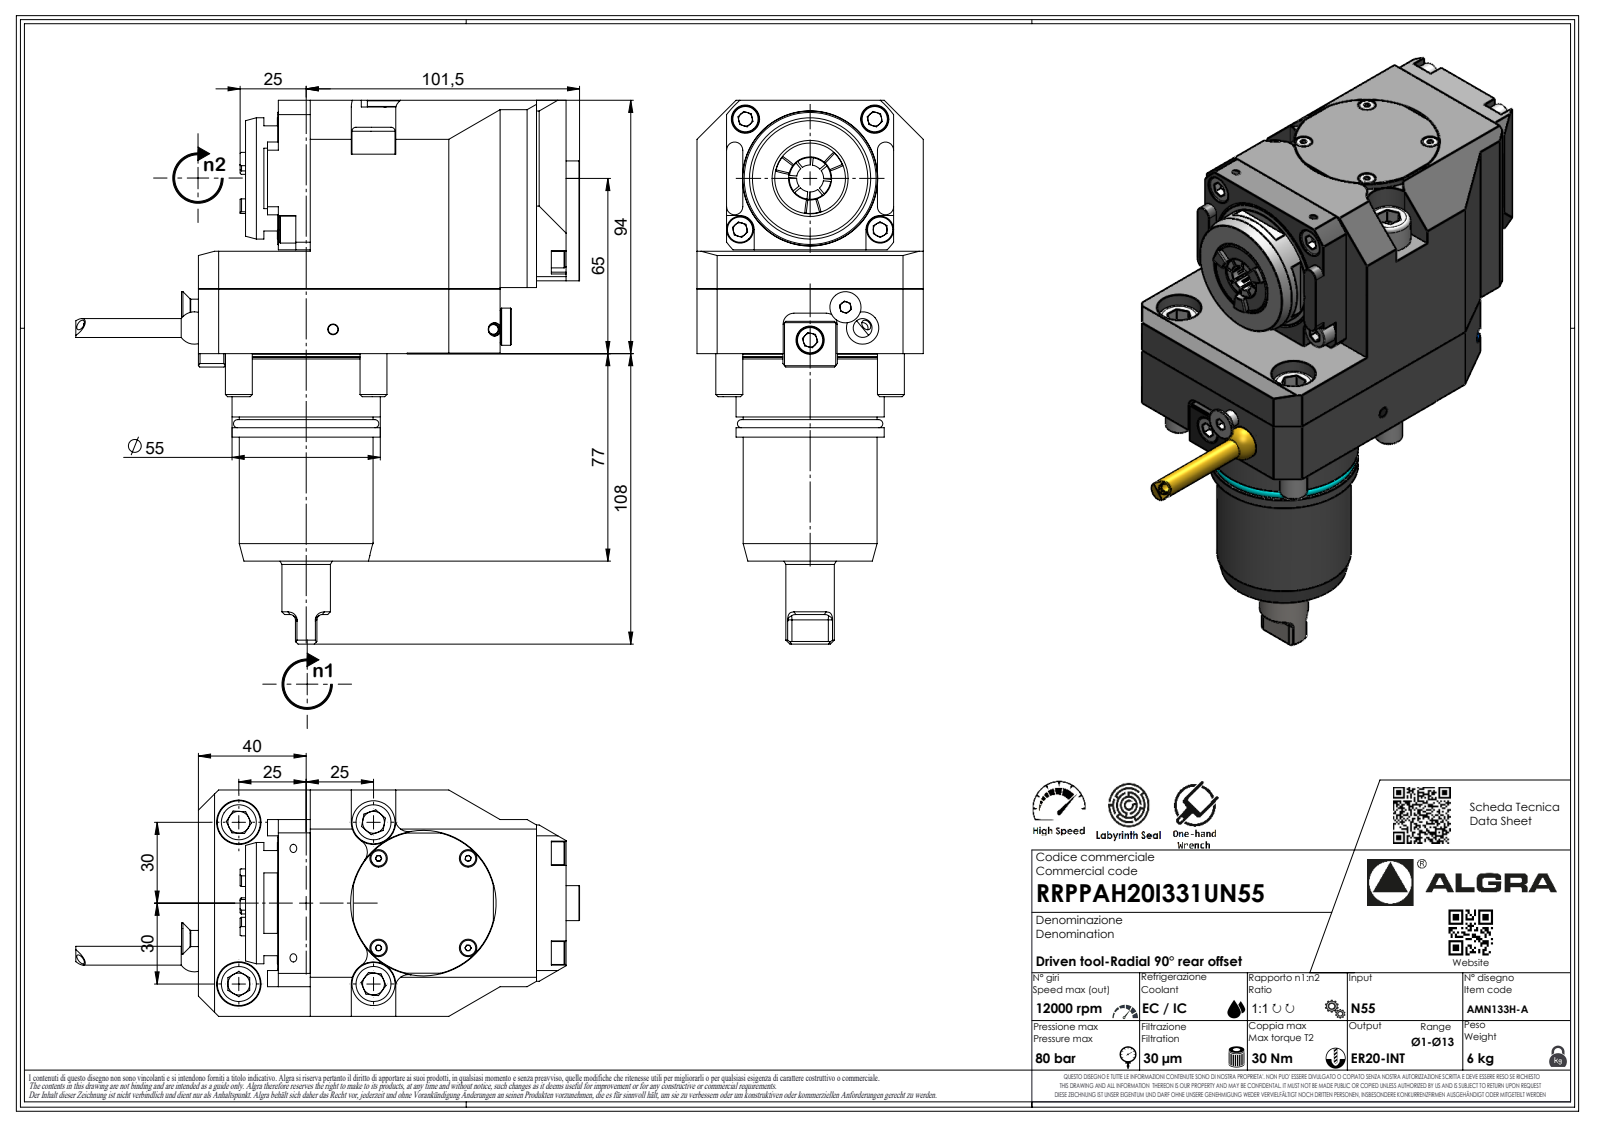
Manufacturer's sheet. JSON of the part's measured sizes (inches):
{"part_name": "RRPPAH20I331UN55", "step_written_by": "SolidWorks 2023 (AUTOMOTIVE_DESIGN)", "units": "inches", "bodies": {"solids": 1, "faces": 537, "planar": 333, "cylindrical": 81, "other": 123}, "overall_size": [7.945, 7.362, 3.307], "volume_in3": 60.02, "surface_area_in2": 120.8, "round_holes": [[0.157, 2], [0.083, 1]], "round_bosses_or_shafts": [[0.394, 4], [2.165, 1], [2.15, 1], [1.957, 1], [1.772, 1], [0.709, 1], [0.276, 1], [0.251, 1]], "partial_cylinders_radius": [[0.079, 8], [0.013, 7], [0.02, 7], [0.146, 7], [0.118, 4], [0.157, 2], [0.197, 2], [0.315, 2]], "face_to_face_distances": [3.307, 0.433, 3.701, 2.205, 1.496, 2.874, 0.965, 1.488, 3.693, 5.374]}
